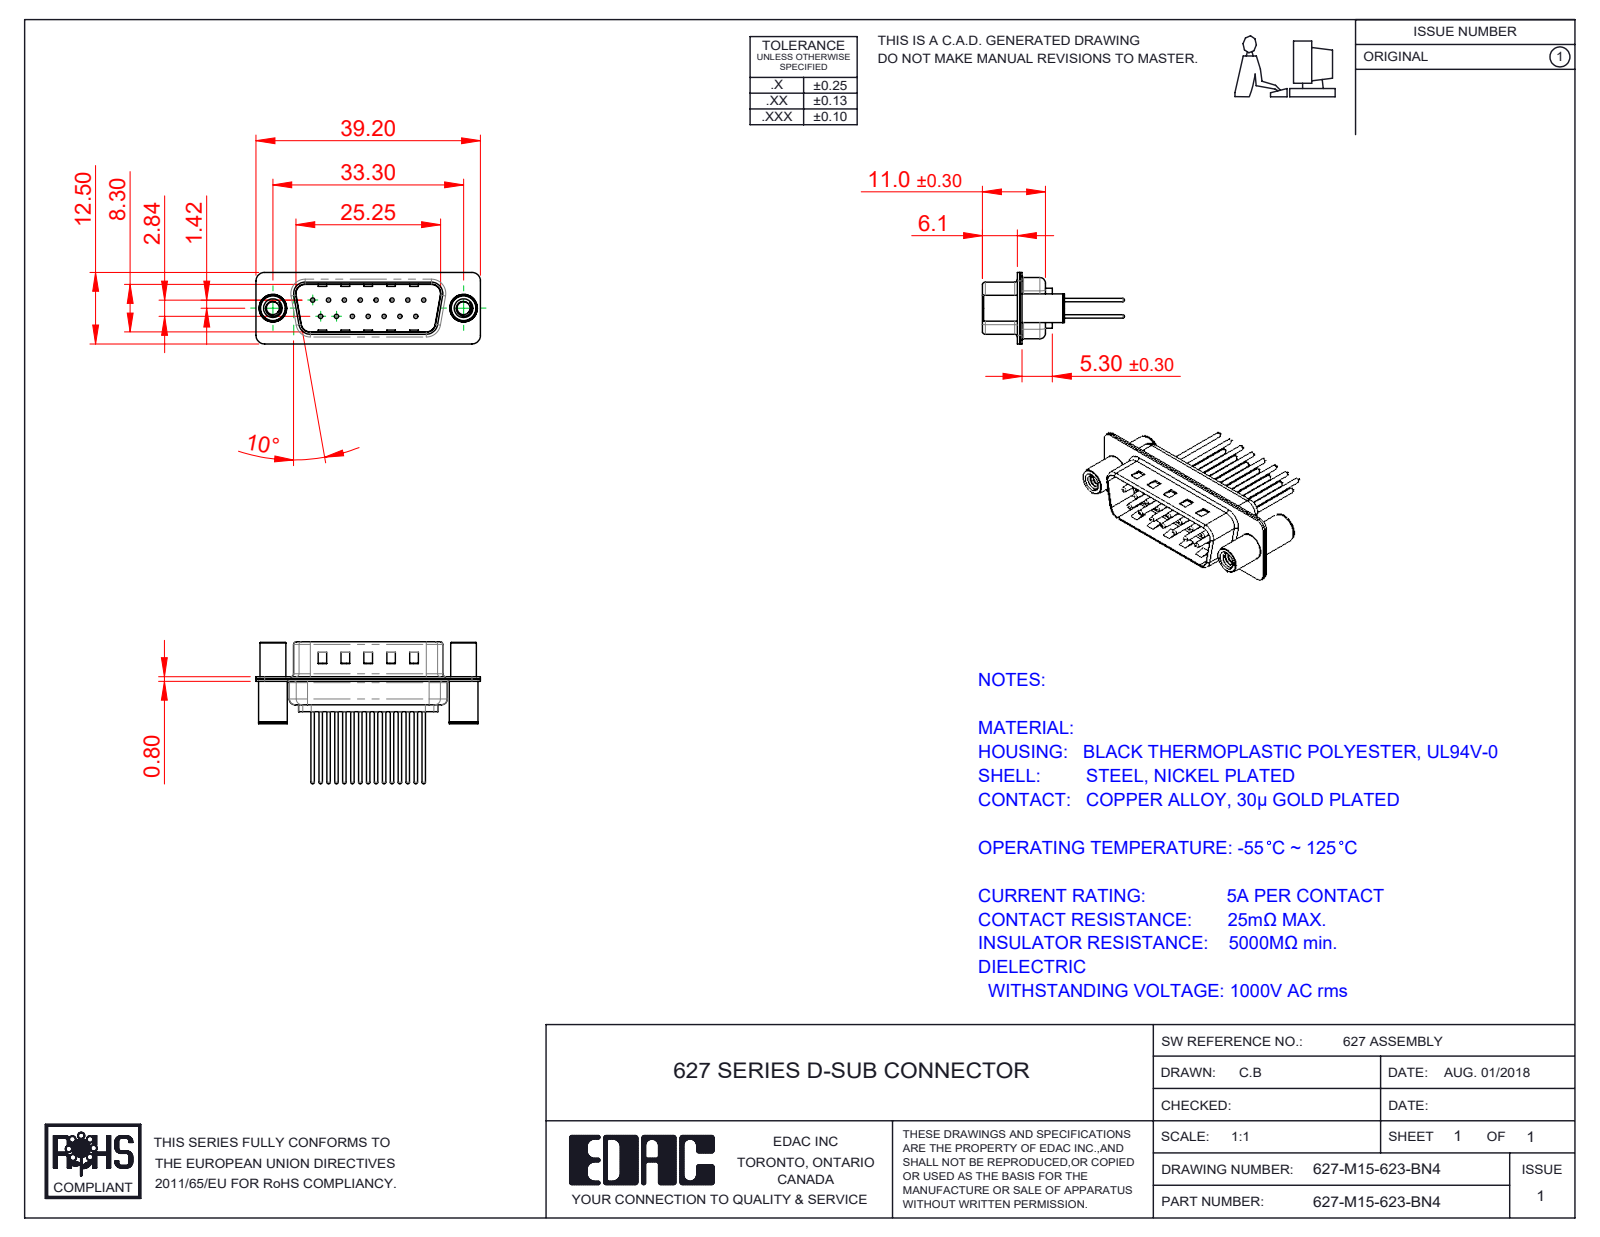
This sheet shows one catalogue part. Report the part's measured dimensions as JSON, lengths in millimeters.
{"part_name": "627M Contact Row 1_23; 627-M15-623-BN4; 627M Contact Row 2_23; 627M Shell Front_15 Contacts (+3 more)", "step_written_by": "SolidWorks 2020 (CONFIG_CONTROL_DESIGN)", "units": "millimeters", "bodies": {"solids": 20, "faces": 981, "planar": 250, "cylindrical": 395, "other": 336}, "overall_size": [39.2, 24.77, 12.5], "volume_mm3": 2159, "surface_area_mm2": 5532, "round_holes": [[0.75, 15], [1.6, 15], [2, 15], [2.26, 2], [3.26, 2], [4, 2], [4.8, 2]], "round_bosses_or_shafts": [[1.5, 15], [0.6, 15], [5, 2], [4.9, 2], [4.5, 2]], "partial_cylinders_radius": [[1.5, 16], [2, 12], [0.5, 8], [1.6, 8], [0.25, 4], [0.6, 4], [0.65, 4], [0.9, 4]], "face_to_face_distances": [0.4, 0.8, 9.5, 9.1, 8.7, 9.9, 1.2, 5.3, 6.1, 5.7], "hole_center_spacings": [3.16, 2.77, 5.54, 8.31, 11.08, 5.03, 5.04, 7.48]}
